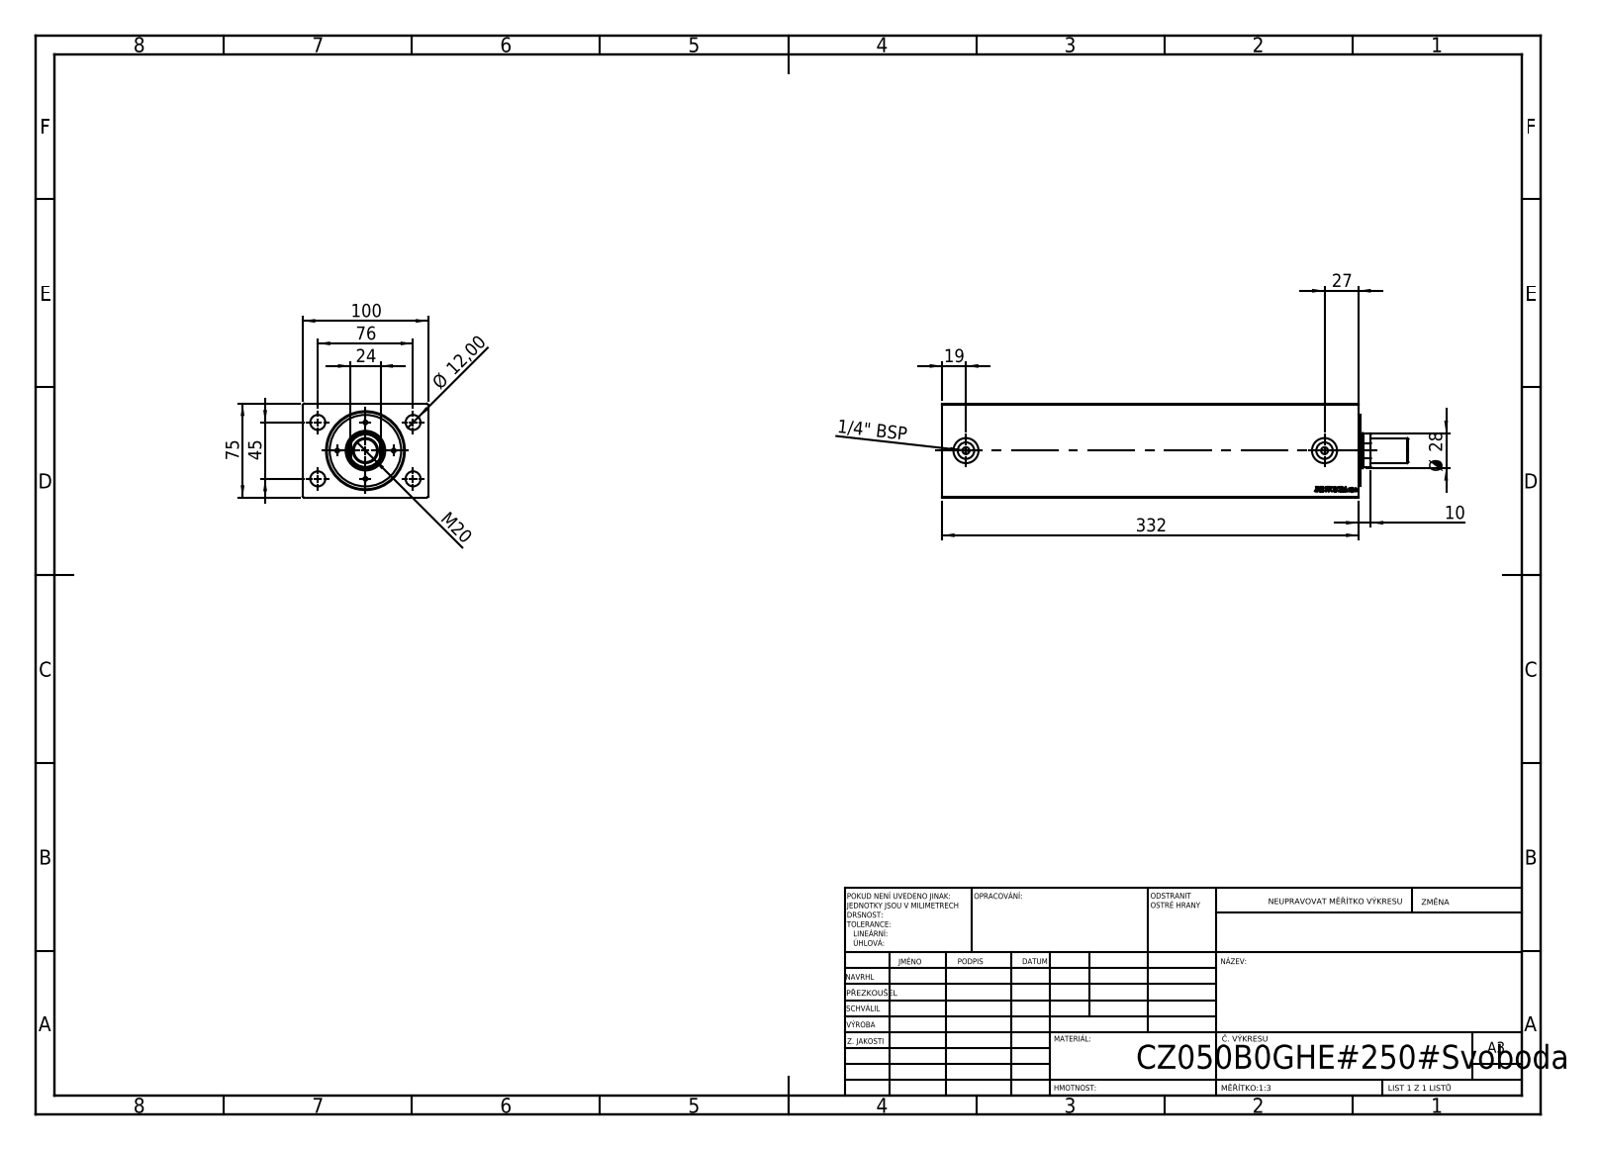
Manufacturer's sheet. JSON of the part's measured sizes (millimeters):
{"part_name": "V500CZ_B_VC; V500CZ_SMALL_MALE_METRIC; V500CZ", "step_written_by": "SolidWorks 2019 (CONFIG_CONTROL_DESIGN)", "units": "millimeters", "bodies": {"solids": 4, "faces": 880, "planar": 402, "cylindrical": 60, "other": 418}, "overall_size": [372, 100, 75], "volume_mm3": 2131000, "surface_area_mm2": 236858, "round_holes": [[3, 4], [12, 4], [5.5, 2], [13.16, 2], [20, 2], [18.5, 1], [28, 1], [29, 1], [36, 1], [50, 1], [61.5, 1]], "round_bosses_or_shafts": [[57, 1], [20, 1]], "partial_cylinders_radius": [[13.5, 1]], "face_to_face_distances": [75, 100, 332, 314.2, 17.8, 10, 8.2, 1.8, 306, 323.8], "hole_center_spacings": [22.5, 27.32, 31.82, 38, 44.16, 45, 58.9, 64.55]}
